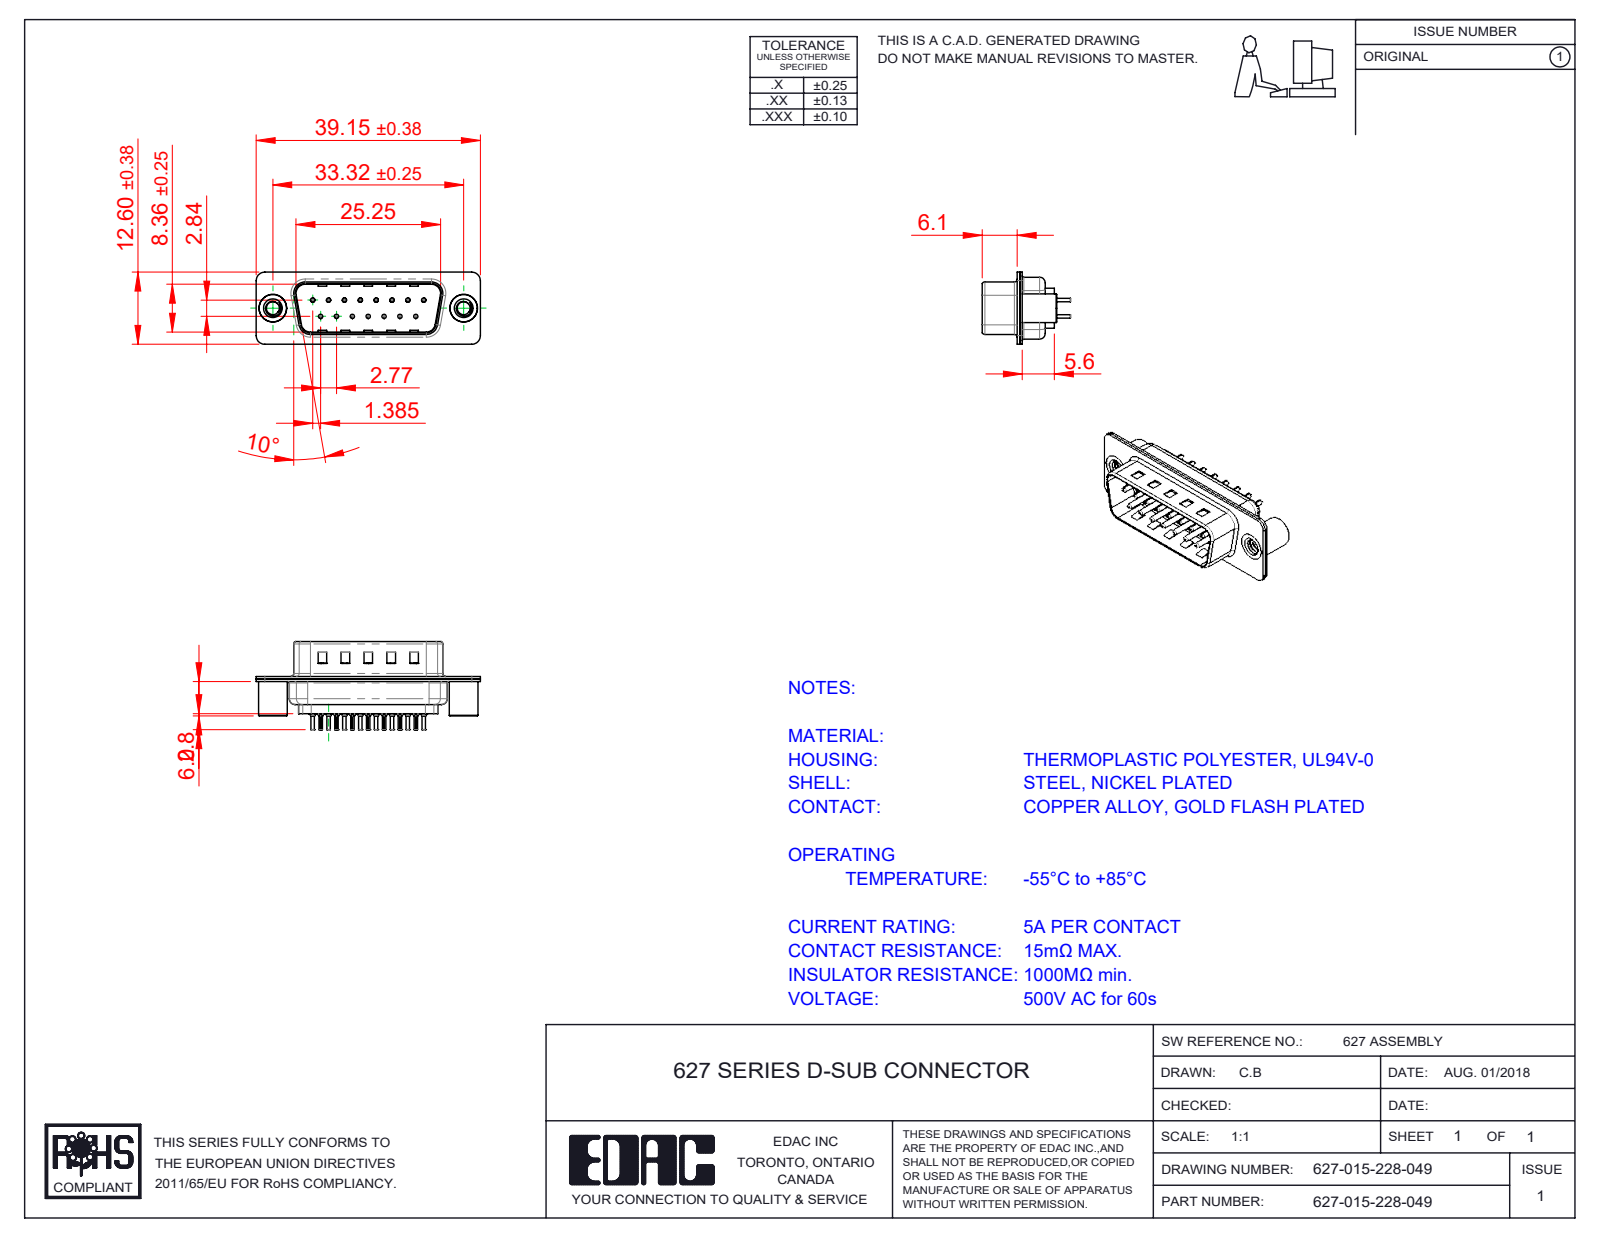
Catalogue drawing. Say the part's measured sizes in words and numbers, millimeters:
The part is named "627 4-40 Threaded Standoff BS; 627 Housing_15 FF; 627-015-228-049; 627 Shell Rear_15 Contacts (+3 more)". Its 3-D file was written by "SolidWorks 2020 (CONFIG_CONTROL_DESIGN)". It is 21 solids with 1873 faces: 505 planar, 743 cylindrical and 625 other. Overall it measures 39.15 by 18.8 by 12.6 millimeters. Its volume is 2 306 cubic millimeters and its surface area 6 290 square millimeters. Round holes: 15 of diameter 0.2, 15 of diameter 0.35, 15 of diameter 1.1, 15 of diameter 1.6, 2 of diameter 2.26, 2 of diameter 4, 2 of diameter 4.8. Round bosses or shafts: 15 of diameter 2, 15 of diameter 1.5, 15 of diameter 0.75, 15 of diameter 0.6, 2 of diameter 5, 2 of diameter 4.9. Partial cylindrical surfaces (rounded edges, fillets, slot ends): 30 of radius 0.1, 16 of radius 1.5, 12 of radius 2, 8 of radius 0.5, 8 of radius 1.6, 4 of radius 0.25, 4 of radius 0.6, 4 of radius 0.65. The main face-to-face distances are 0.4, 0.45, 0.9, 6.05, 0.82, 9.58, 8.4, 6.5, 1.5, 2.8. The hole center spacings are 3.16, 2.77, 5.54, 8.31, 11.08, 5.03, 5.04, 7.48.
